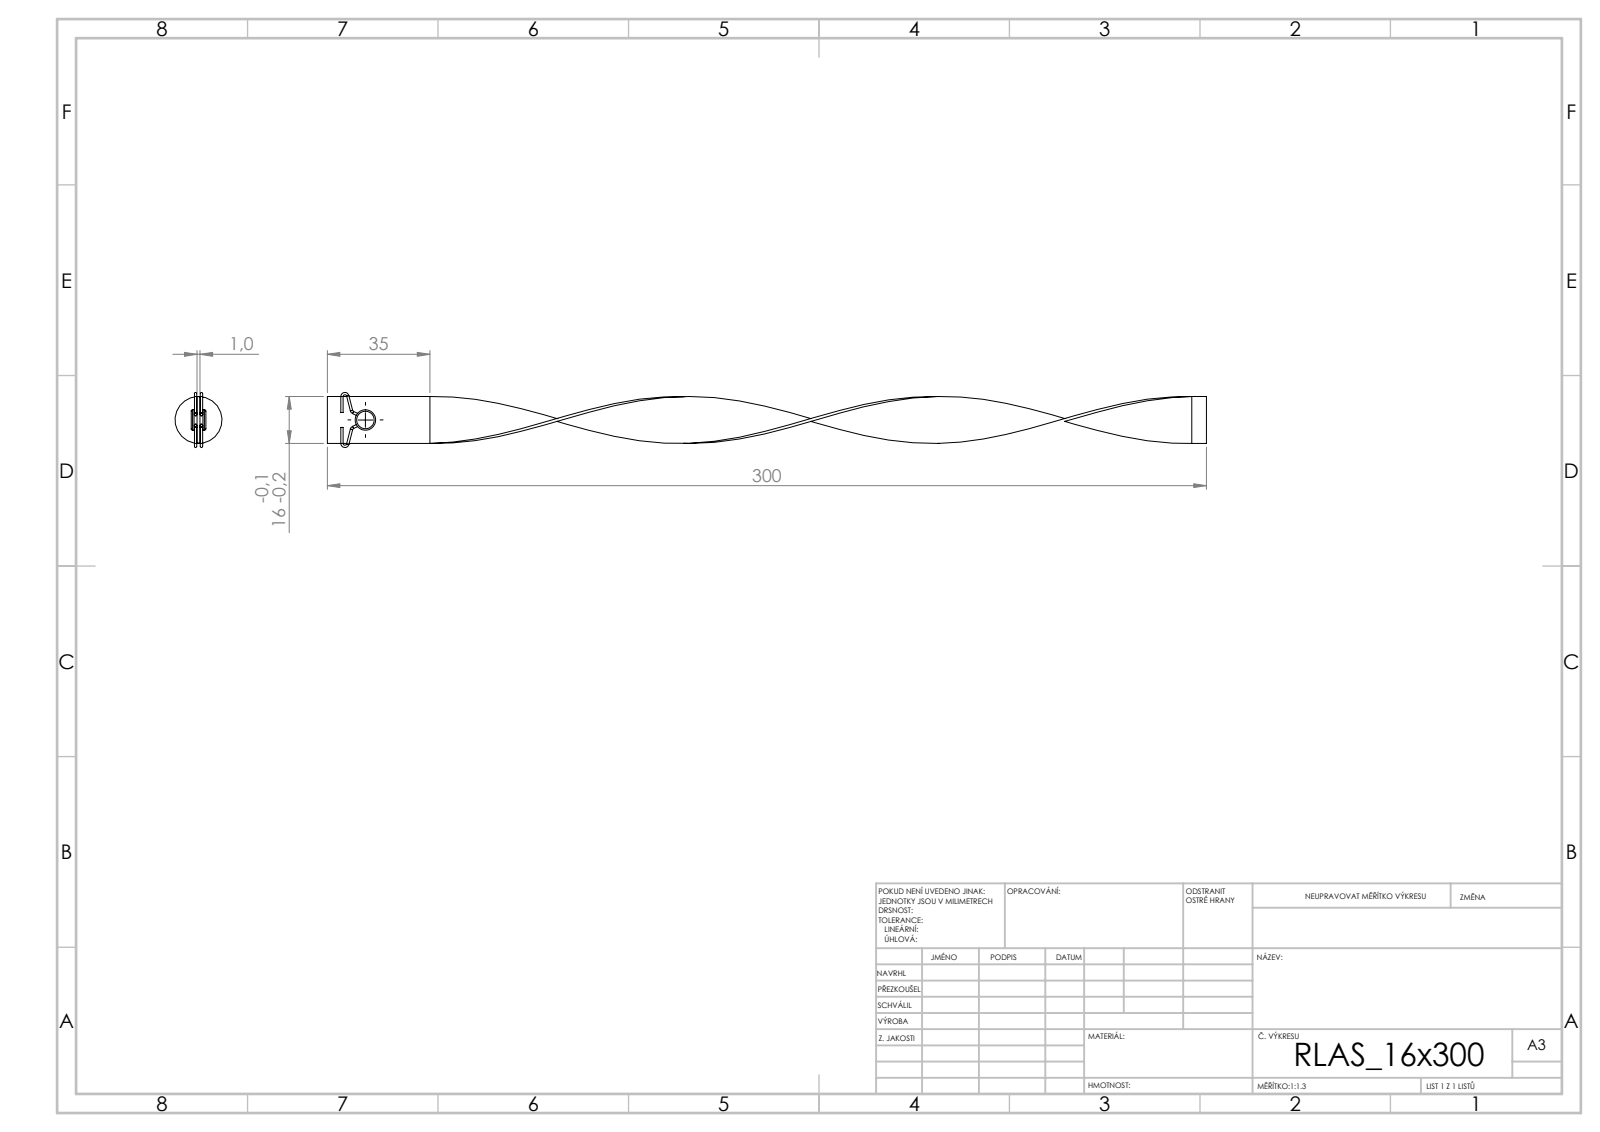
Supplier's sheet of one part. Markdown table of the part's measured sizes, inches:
| quantity | value |
| --- | --- |
| STEP written by | SolidWorks 2019 (CONFIG_CONTROL_DESIGN) |
| units | inches |
| bodies | 3 solids, 90 faces (18 planar, 40 cylindrical, 32 other) |
| overall size | 11.811 × 0.74 × 0.631 |
| volume | 0.302 in³ |
| surface area | 16.65 in² |
| round bosses / shafts (diameter × count) | 0.031 × 14, 0.276 × 1, 0.157 × 1 |
| main face-to-face distances | 0.039, 0.079, 0.118, 0.157, 0.63, 0.197, 11.811, 0.215, 0.415, 0.201 |
